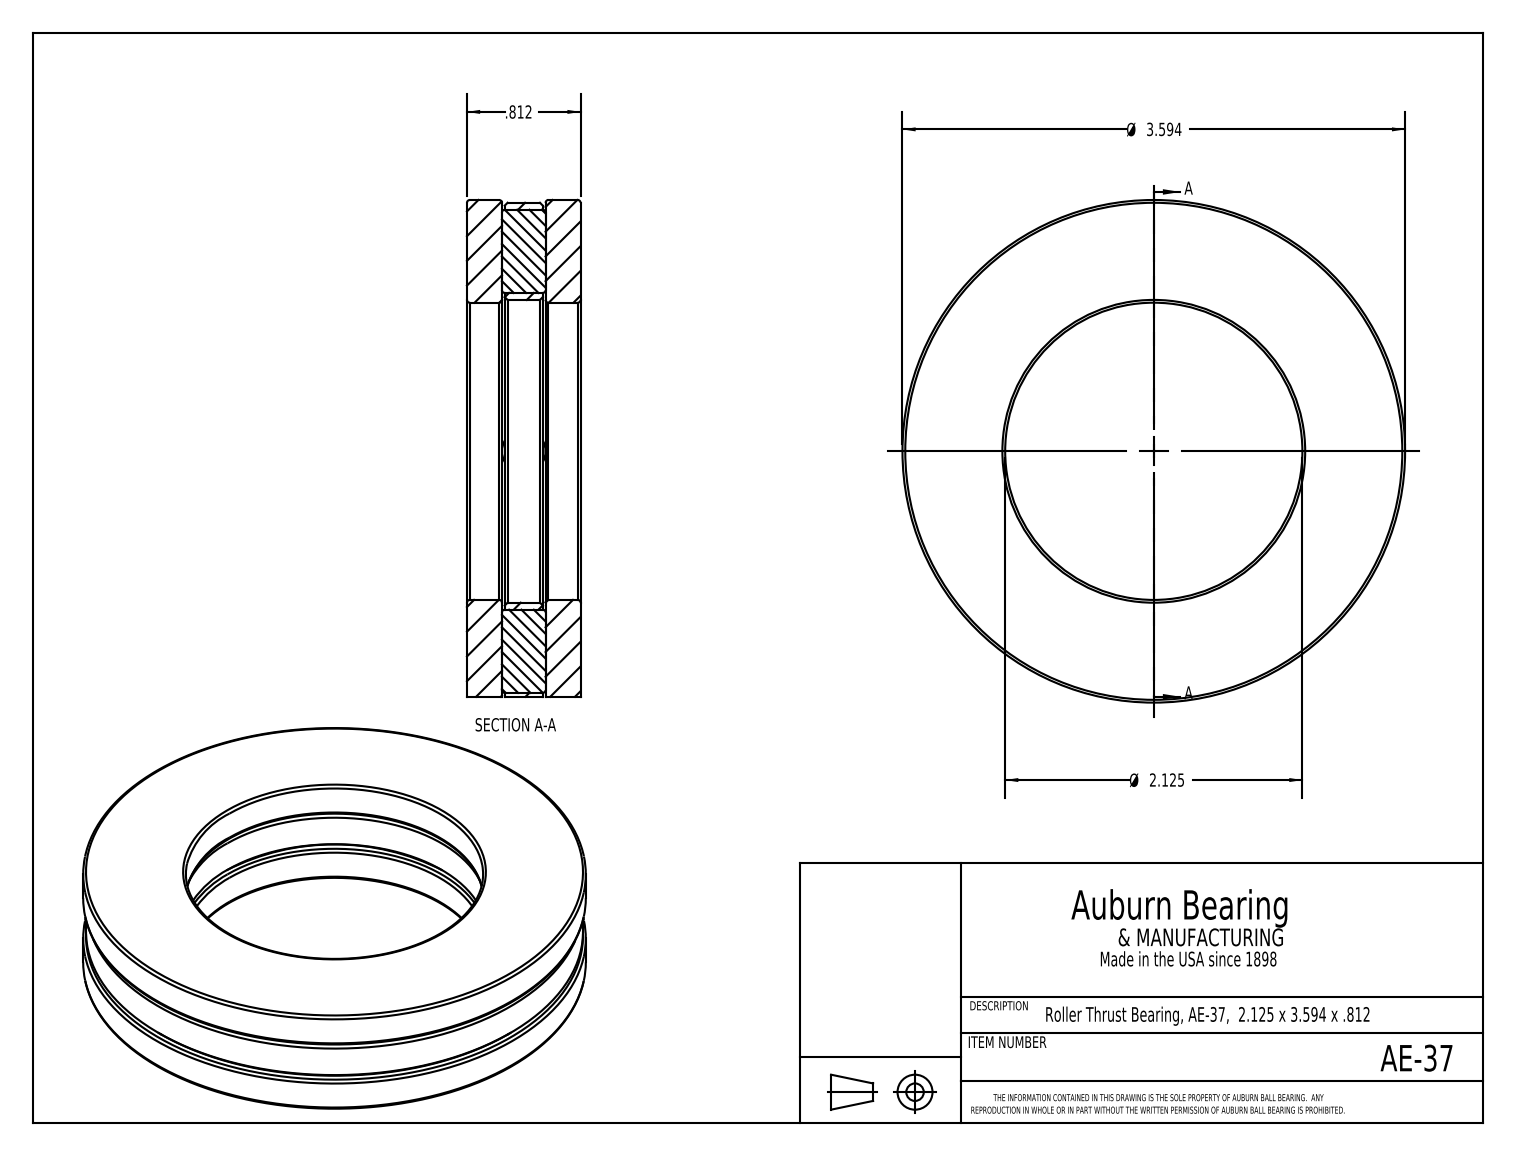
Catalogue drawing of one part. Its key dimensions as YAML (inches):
part_name: "AE-37"
step_written_by: "SolidWorks 2017 (CONFIG_CONTROL_DESIGN)"
units: inches
bodies: {solids: 7, faces: 60, planar: 30, cylindrical: 10, other: 20}
overall_size: [3.594, 3.594, 0.812]
volume: 4.961
surface_area: 55.06
round_holes:
  - {diameter: 2.125, count: 1}
  - {diameter: 2.165, count: 1}
round_bosses_or_shafts:
  - {diameter: 0.312, count: 2}
  - {diameter: 3.594, count: 1}
  - {diameter: 3.554, count: 1}
face_to_face_distances: [0.25, 0.562, 0.27, 0.542, 0.02, 0.292, 0.312, 0.812, 0.272, 0.977]
